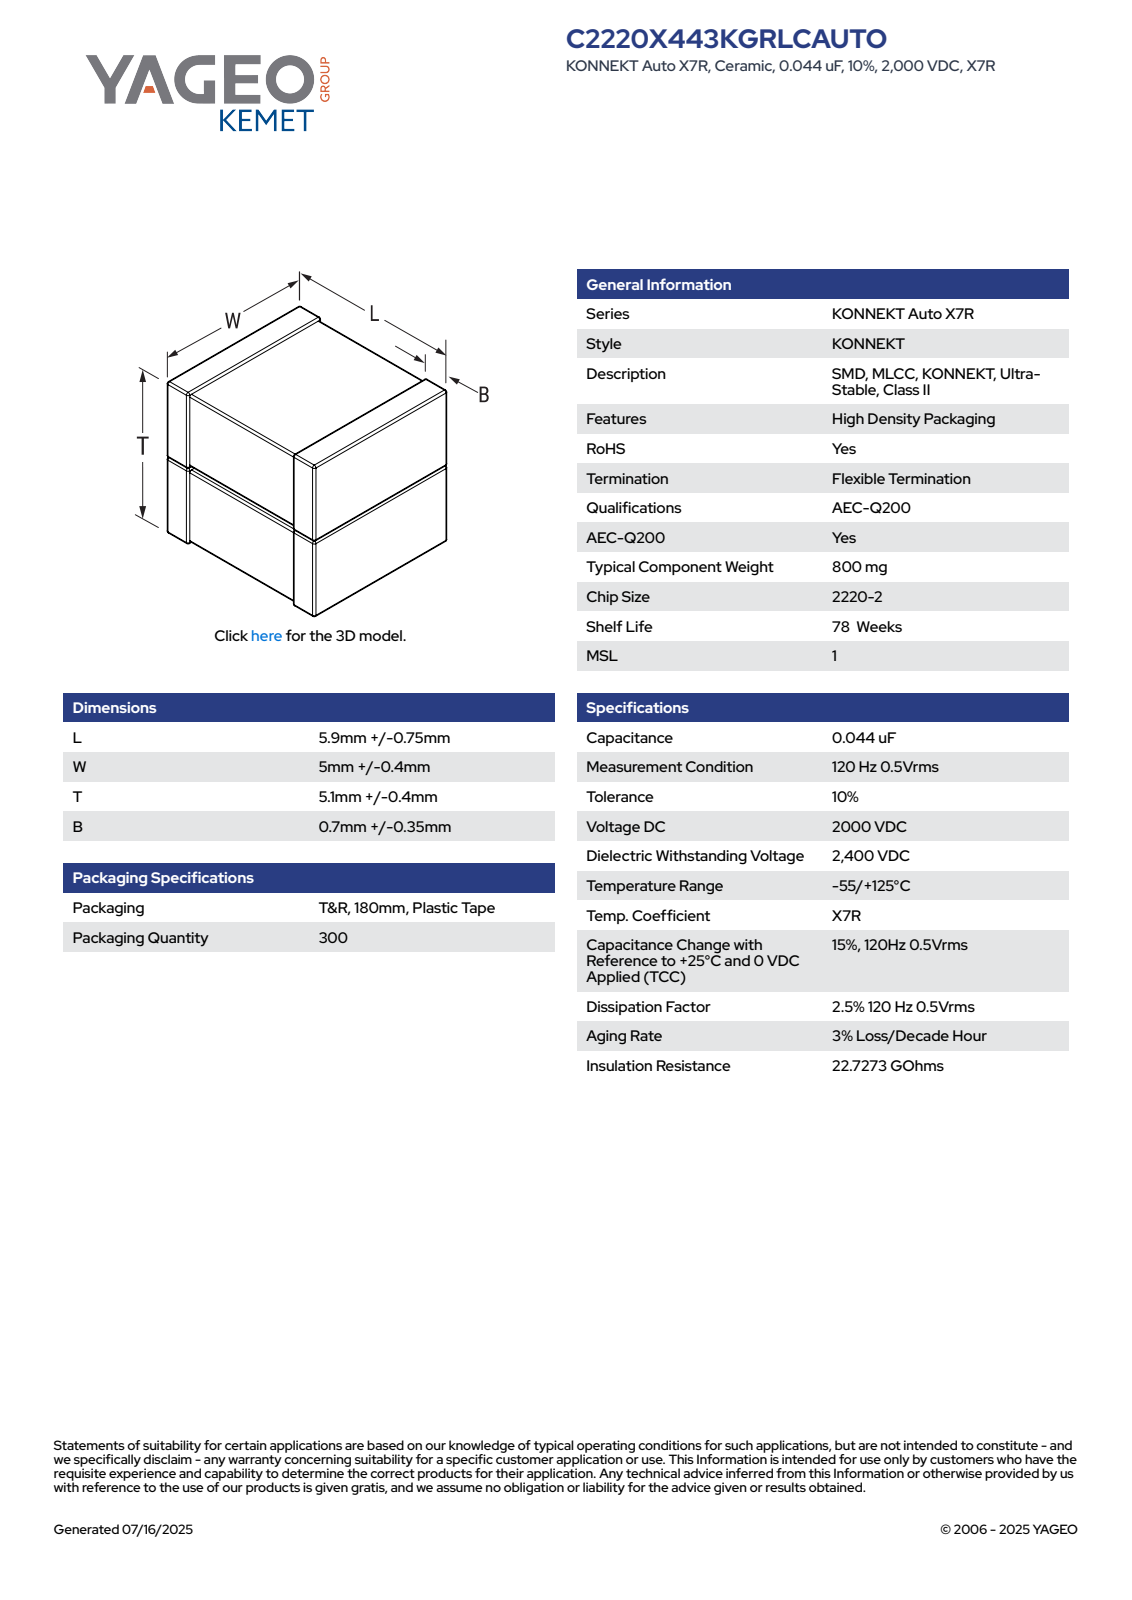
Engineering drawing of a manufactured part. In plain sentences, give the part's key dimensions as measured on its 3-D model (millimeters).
The part is named "CCSS_K2T_2220-2_L6.65W5.4B1.05T5.5". Its 3-D file was written by "SolidWorks 2020 (AUTOMOTIVE_DESIGN)". It is 4 solids with 181 faces: 81 planar, 68 cylindrical and 32 other. Overall it measures 6.65 by 5.5 by 5.4 millimeters. Its volume is 187 cubic millimeters and its surface area 254 square millimeters. The main face-to-face distances are 2.61, 2.75, 6.65, 5.36, 5.26, 2.68, 2.82, 5.43, 5.33, 5.5.
